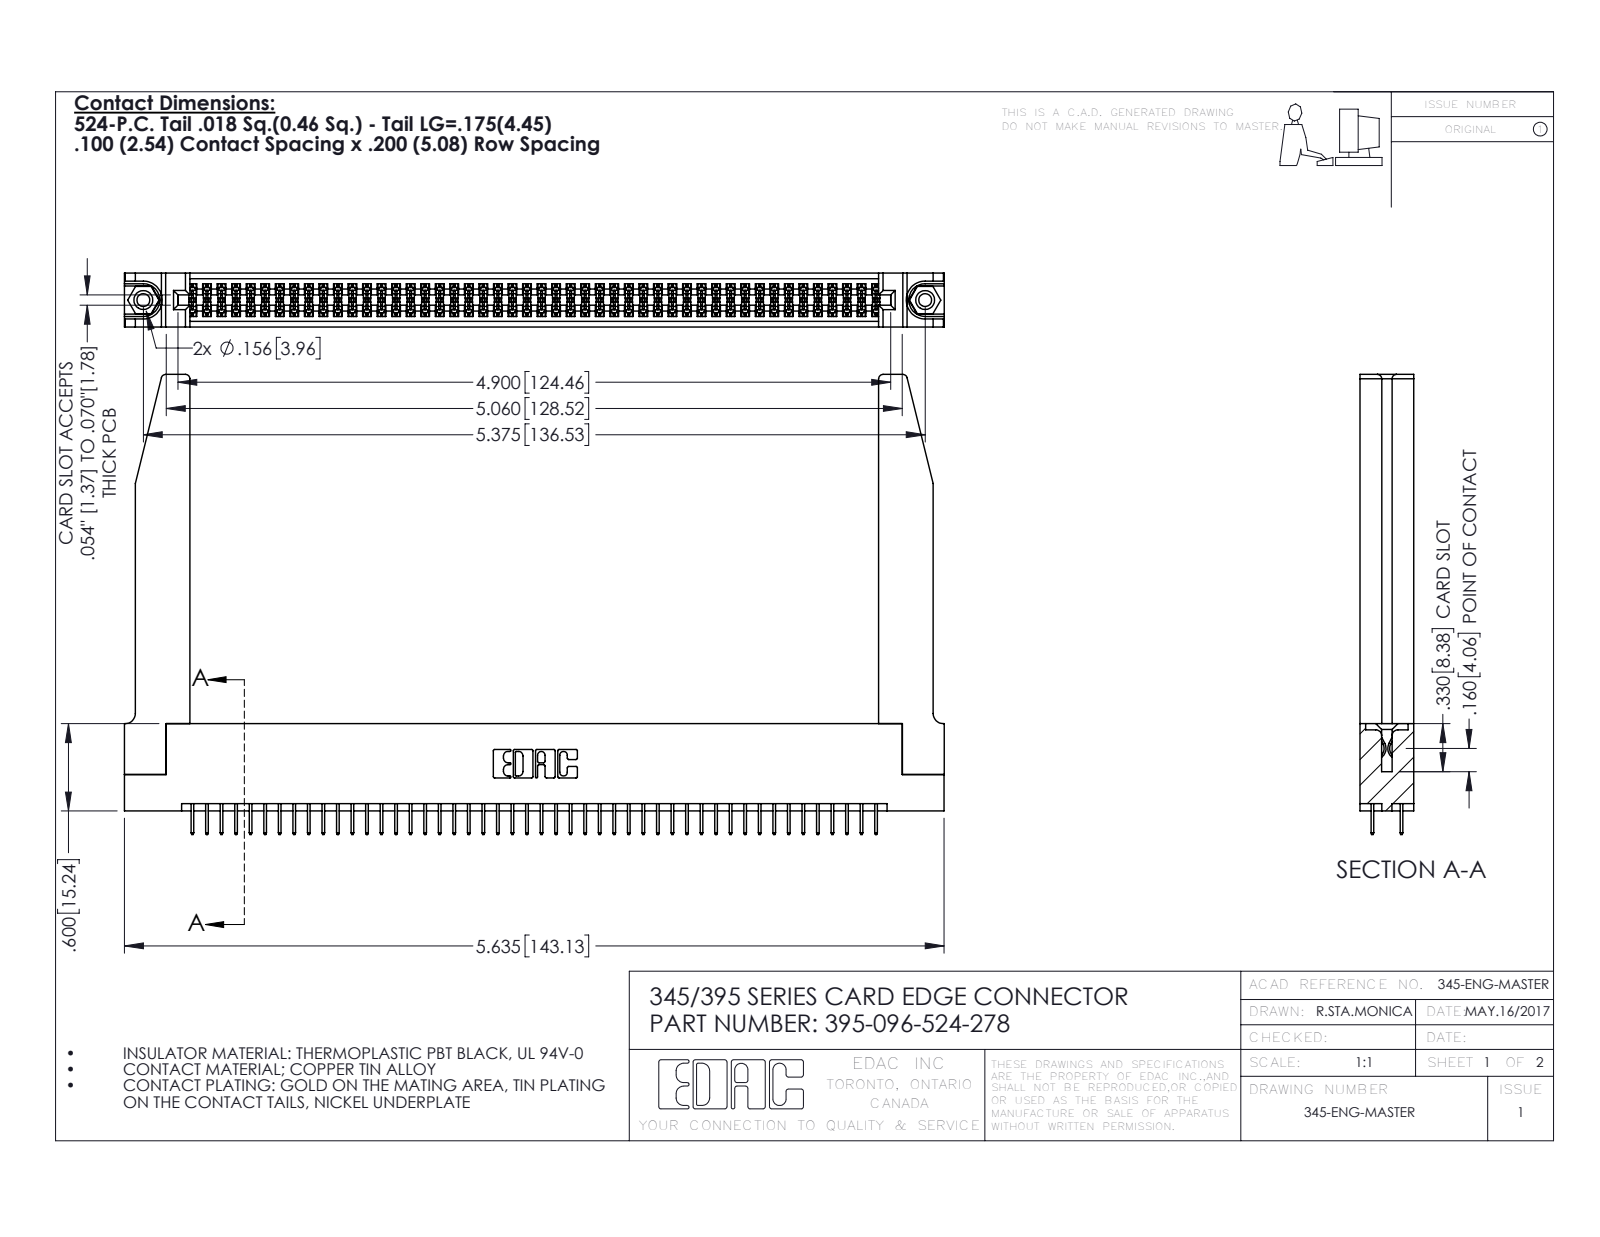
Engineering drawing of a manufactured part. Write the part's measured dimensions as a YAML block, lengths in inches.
part_name: "345-220-078_345-220-078; 345 Part_Flush Mounting Lugs - 0.156 Dia-TH; 345-250-001_345-250-001-102; 395-096-524-278 (+1 more)"
step_written_by: "SolidWorks 2016 (CONFIG_CONTROL_DESIGN)"
units: inches
bodies: {solids: 101, faces: 5544, planar: 3966, cylindrical: 1526, other: 52}
overall_size: [5.636, 3.162, 0.37]
volume: 1.317
surface_area: 41.84
round_holes:
  - {diameter: 0.089, count: 2}
  - {diameter: 0.125, count: 2}
  - {diameter: 0.156, count: 2}
  - {diameter: 0.064, count: 1}
round_bosses_or_shafts:
  - {diameter: 0.155, count: 2}
partial_cylinders:
  - {radius: 0.006, count: 144}
  - {radius: 0.01, count: 22}
  - {radius: 0.03, count: 8}
  - {radius: 0.007, count: 6}
  - {radius: 0.031, count: 6}
  - {radius: 0.026, count: 3}
  - {radius: 0.014, count: 2}
  - {radius: 0.019, count: 2}
face_to_face_distances: [0.37, 0.072, 0.298, 0.2, 0.098, 0.272, 0.025, 0.225, 0.072, 0.15]
hole_center_spacings: [0.27, 5.139, 5.375]
